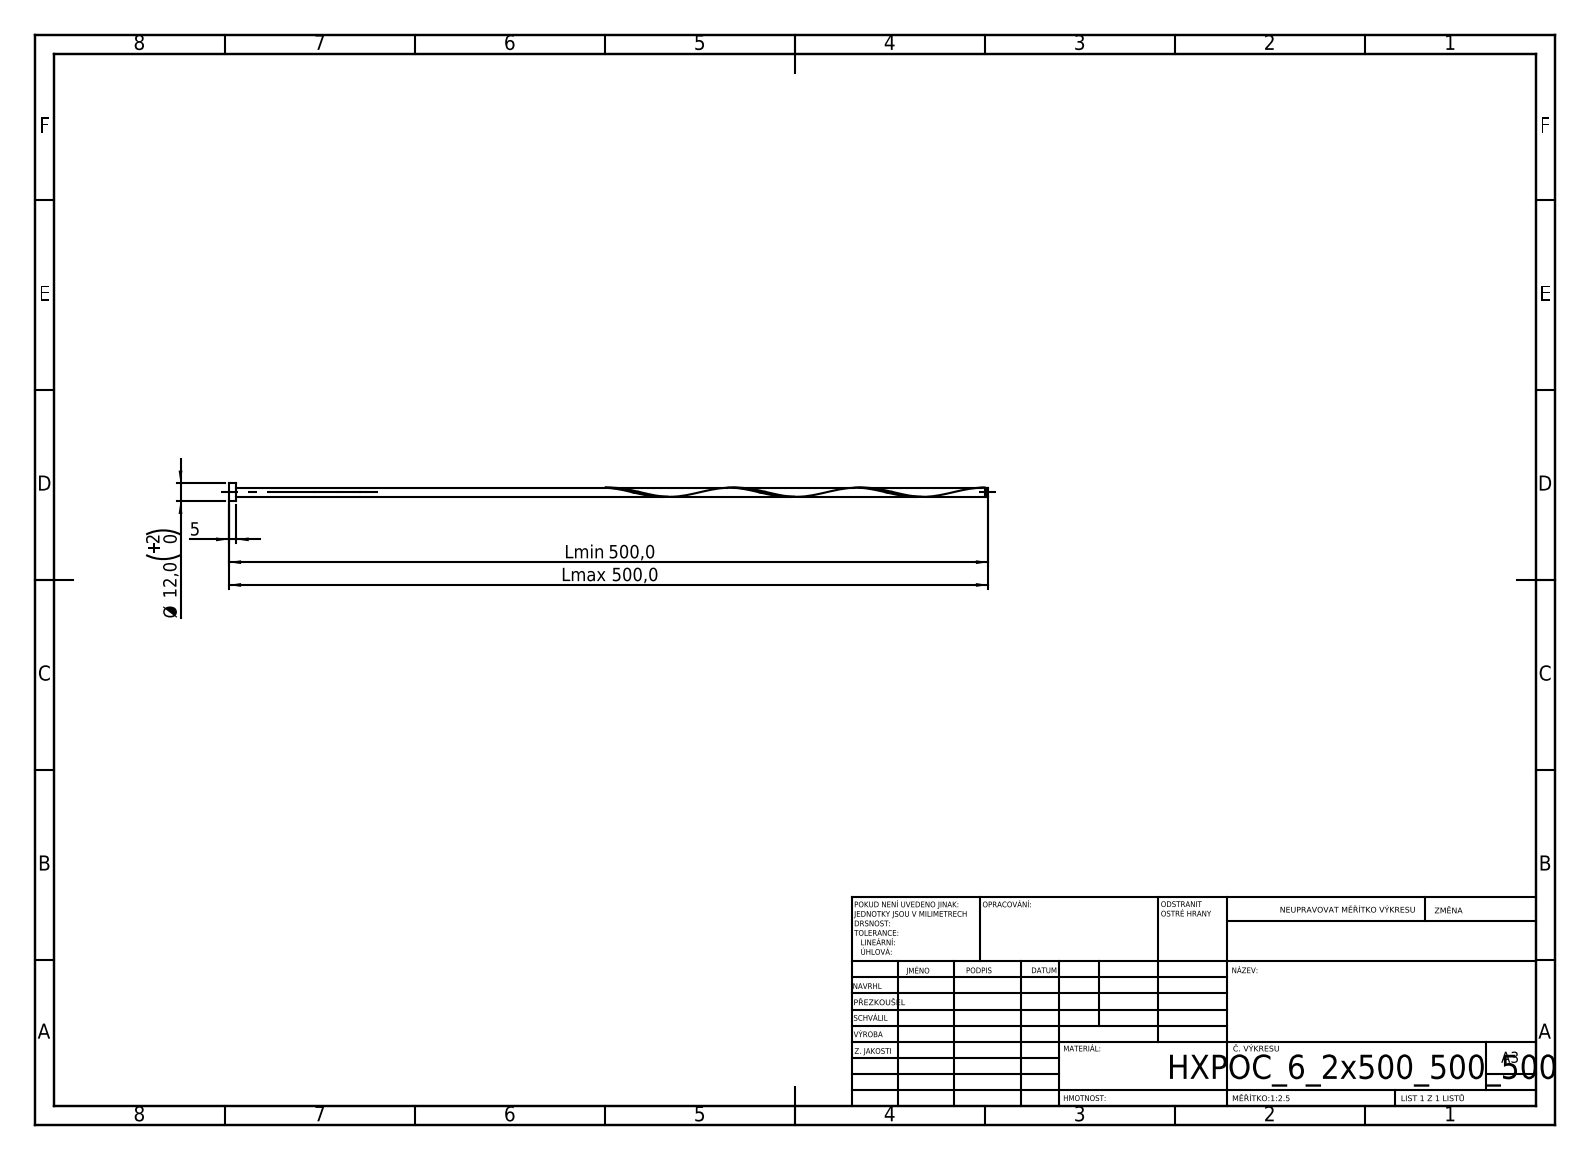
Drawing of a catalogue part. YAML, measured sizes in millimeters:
step_written_by: "SolidWorks 2019 (CONFIG_CONTROL_DESIGN)"
units: millimeters
bodies: {solids: 1, faces: 16, planar: 6, cylindrical: 9, other: 1}
overall_size: [500, 12, 12]
volume: 18706
surface_area: 13470
round_bosses_or_shafts:
  - {diameter: 12, count: 1}
  - {diameter: 6.2, count: 1}
  - {diameter: 4.96, count: 1}
face_to_face_distances: [5, 500, 495, 498.8, 493.8, 1.2, 497.56, 492.56, 1.24, 2.44]
